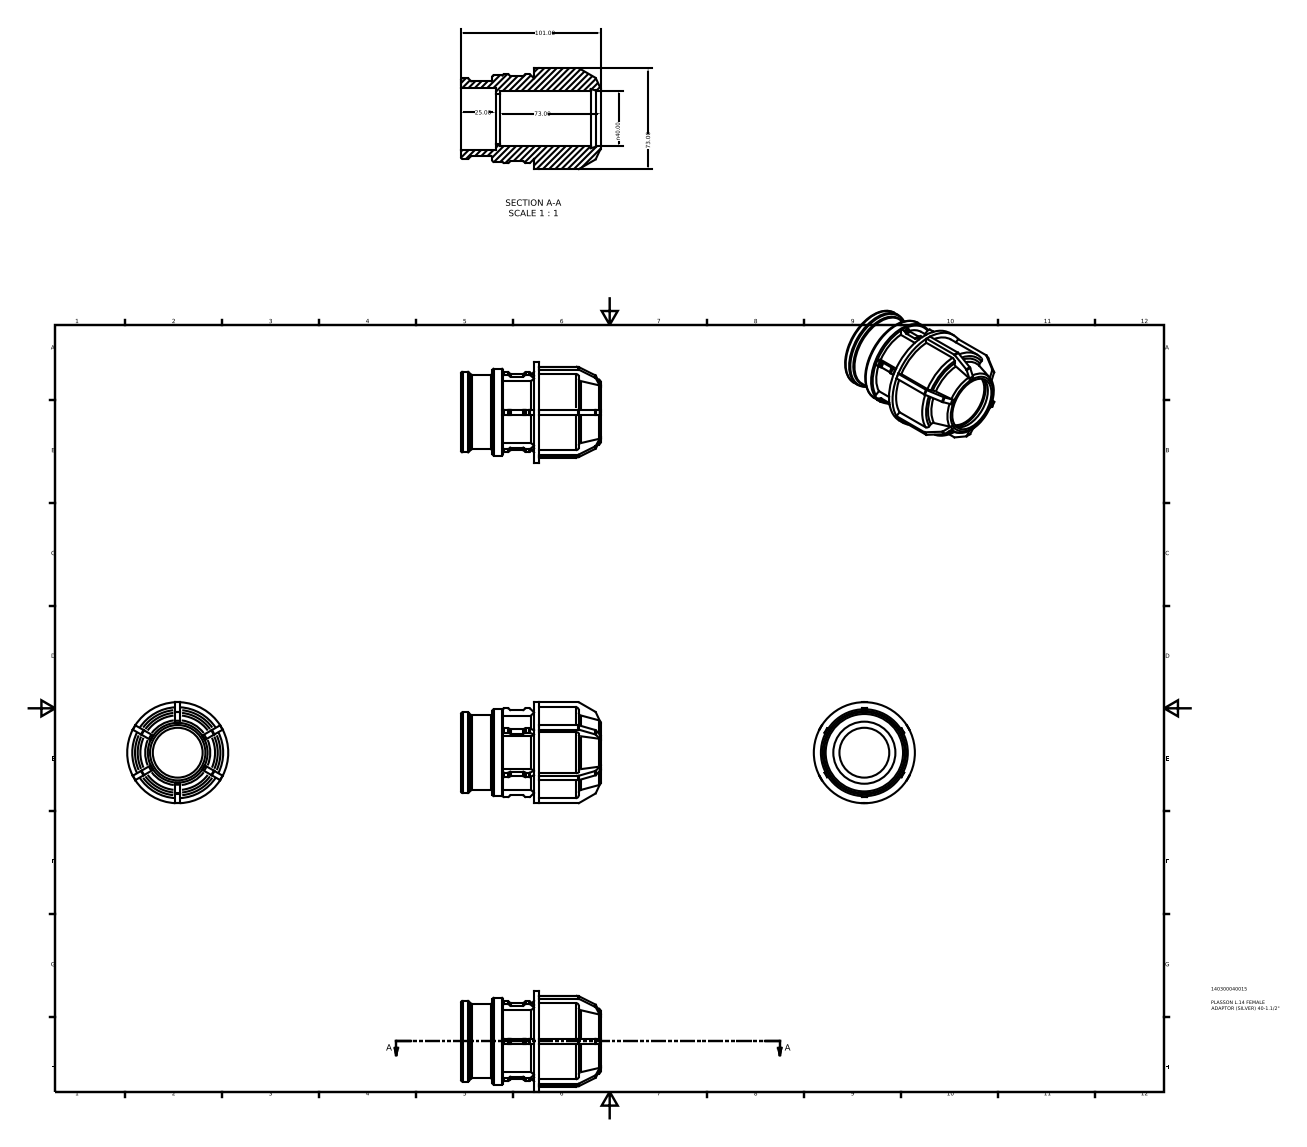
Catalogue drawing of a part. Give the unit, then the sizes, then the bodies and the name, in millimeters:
Units: millimetres
Overall size (bounding box): 101 × 73 × 73
Round holes (diameter × count): ⌀36 ×1, ⌀40 ×1, ⌀44.84 ×1
Round bosses / shafts (diameter × count): ⌀73 ×1, ⌀65.7 ×1, ⌀62.78 ×1, ⌀58.3 ×1, ⌀53.81 ×1
Partial cylindrical surfaces — rounded edges, fillets, slot ends (radius × count): R1.2 ×48
Main face-to-face distances: 3.65, 3.64, 52.82, 5.25, 56.47, 2.25, 3.66, 30.25, 22.57, 26.22
Volume: 145 034 mm³ · Surface area: 42 334 mm²
Bodies: 1 solid, 261 faces (159 planar, 68 cylindrical, 34 other)
Part name (STEP PRODUCT): 140300040015
STEP written by: Autodesk Inventor 2015 (AUTOMOTIVE_DESIGN)
